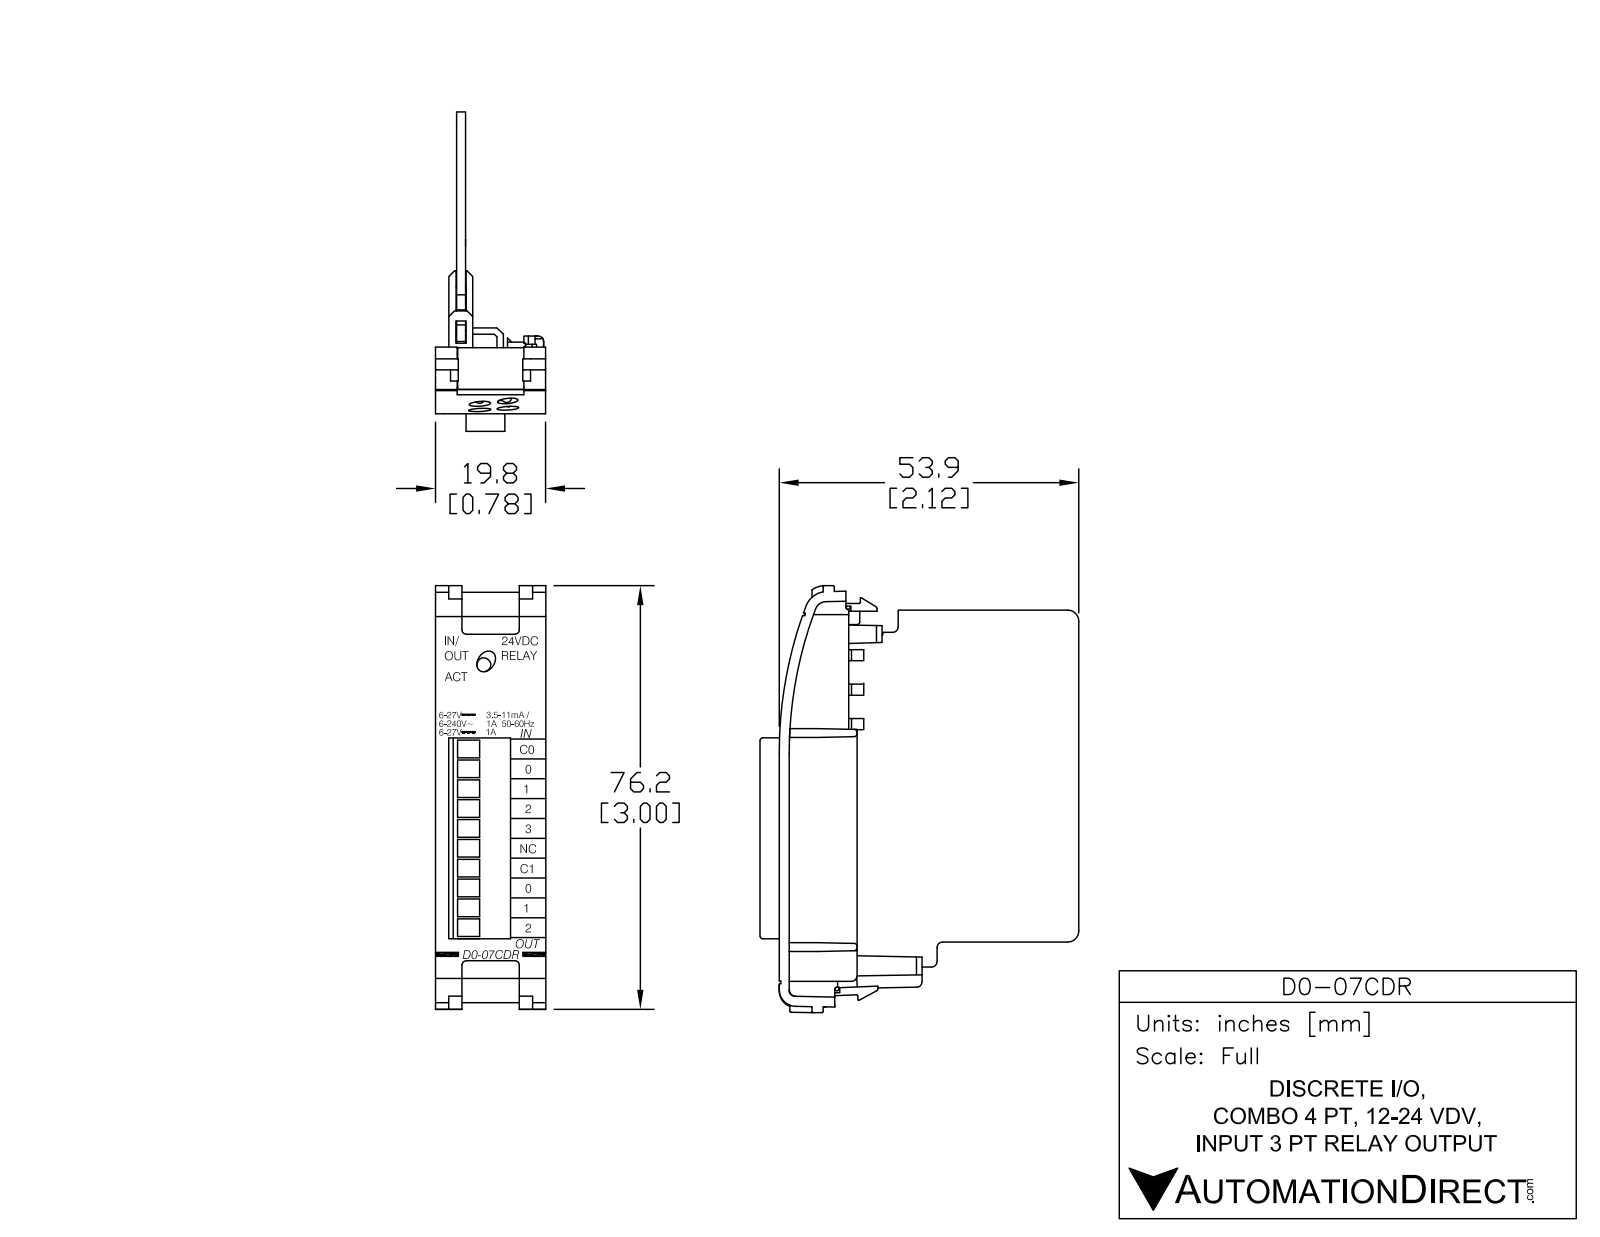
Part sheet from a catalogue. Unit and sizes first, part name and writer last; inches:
Units: inches
Overall size (bounding box): 3.08 × 2.602 × 0.826
Round bosses / shafts (diameter × count): ⌀0.089 ×1
Partial cylindrical surfaces — rounded edges, fillets, slot ends (radius × count): R0.005 ×4, R0.02 ×3, R0.035 ×3, R0.025 ×2, R0.01 ×1, R0.065 ×1, R0.07 ×1, R0.1 ×1
Main face-to-face distances: 0.063, 0.631, 0.05, 0.075, 0.113, 0.581, 0.519, 0.681, 0.569, 0.195
Volume: 0.755 in³ · Surface area: 23.22 in²
Bodies: 2 solids, 333 faces (248 planar, 37 cylindrical, 48 other)
Part name (STEP PRODUCT): D0-07CDR
STEP written by: SolidWorks 2009 (AUTOMOTIVE_DESIGN)
